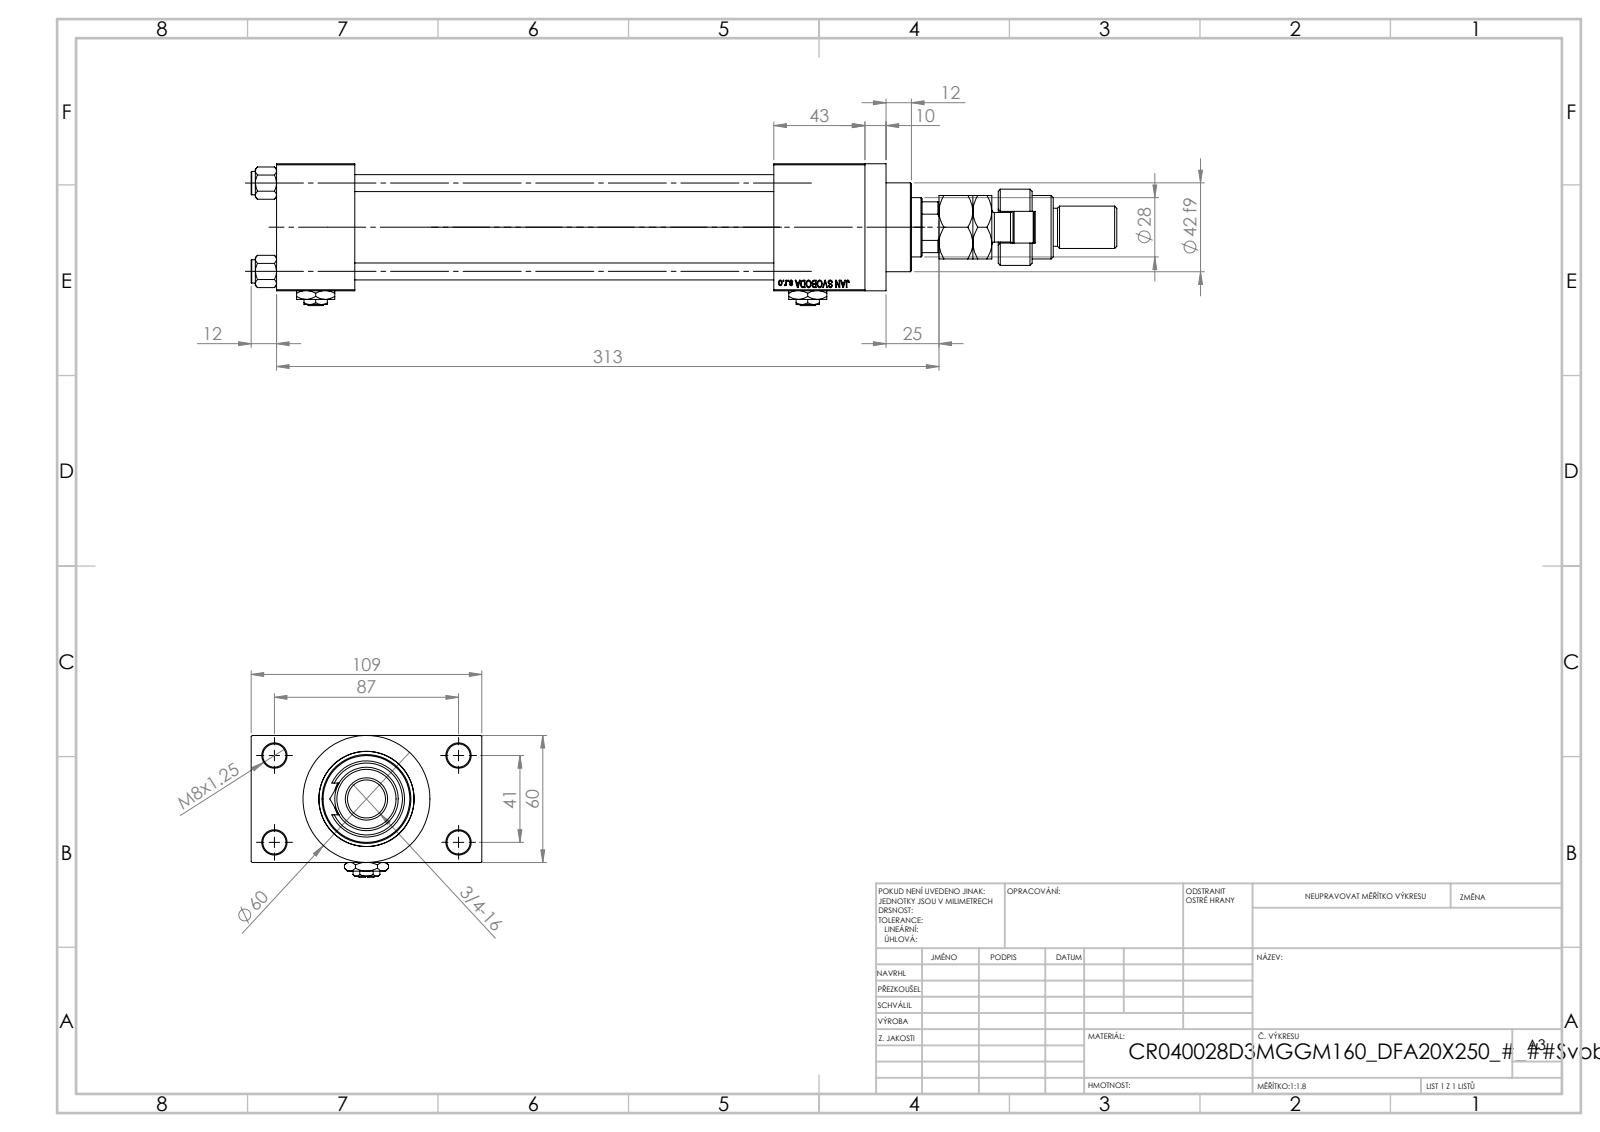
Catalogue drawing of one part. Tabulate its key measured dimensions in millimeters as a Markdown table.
| quantity | value |
| --- | --- |
| part name | FEMALE_PART_FOR_DFA; Zatka_pro_OIL_PORT; V215CR_D_Body; V215CR_D_TYCINKA (+4 more) |
| STEP written by | SolidWorks 2019 (CONFIG_CONTROL_DESIGN) |
| units | millimeters |
| bodies | 15 solids, 1291 faces (574 planar, 113 cylindrical, 604 other) |
| overall size | 409 × 109 × 67 |
| volume | 751 956 mm³ |
| surface area | 207 932 mm² |
| round holes (diameter × count) | 8 × 4, 11 × 4, 7 × 2, 16.66 × 2, 24 × 2, 18.5 × 1, 28 × 1, 31 × 1, 40 × 1, 45 × 1 |
| round bosses / shafts (diameter × count) | 11 × 4, 60 × 1, 46 × 1, 42 × 1, 36 × 1, 30 × 1, 22 × 1, 20 × 1 |
| partial cylindrical surfaces (radius × count) | 7.5 × 1, 12 × 1, 13.5 × 1 |
| main face-to-face distances | 60, 24.5, 84.5, 198, 37, 235, 43, 278, 241, 109 |
| hole center spacings | 22.65, 29.49, 41.7, 47.15, 48.09, 64.35, 76.49, 41 |
